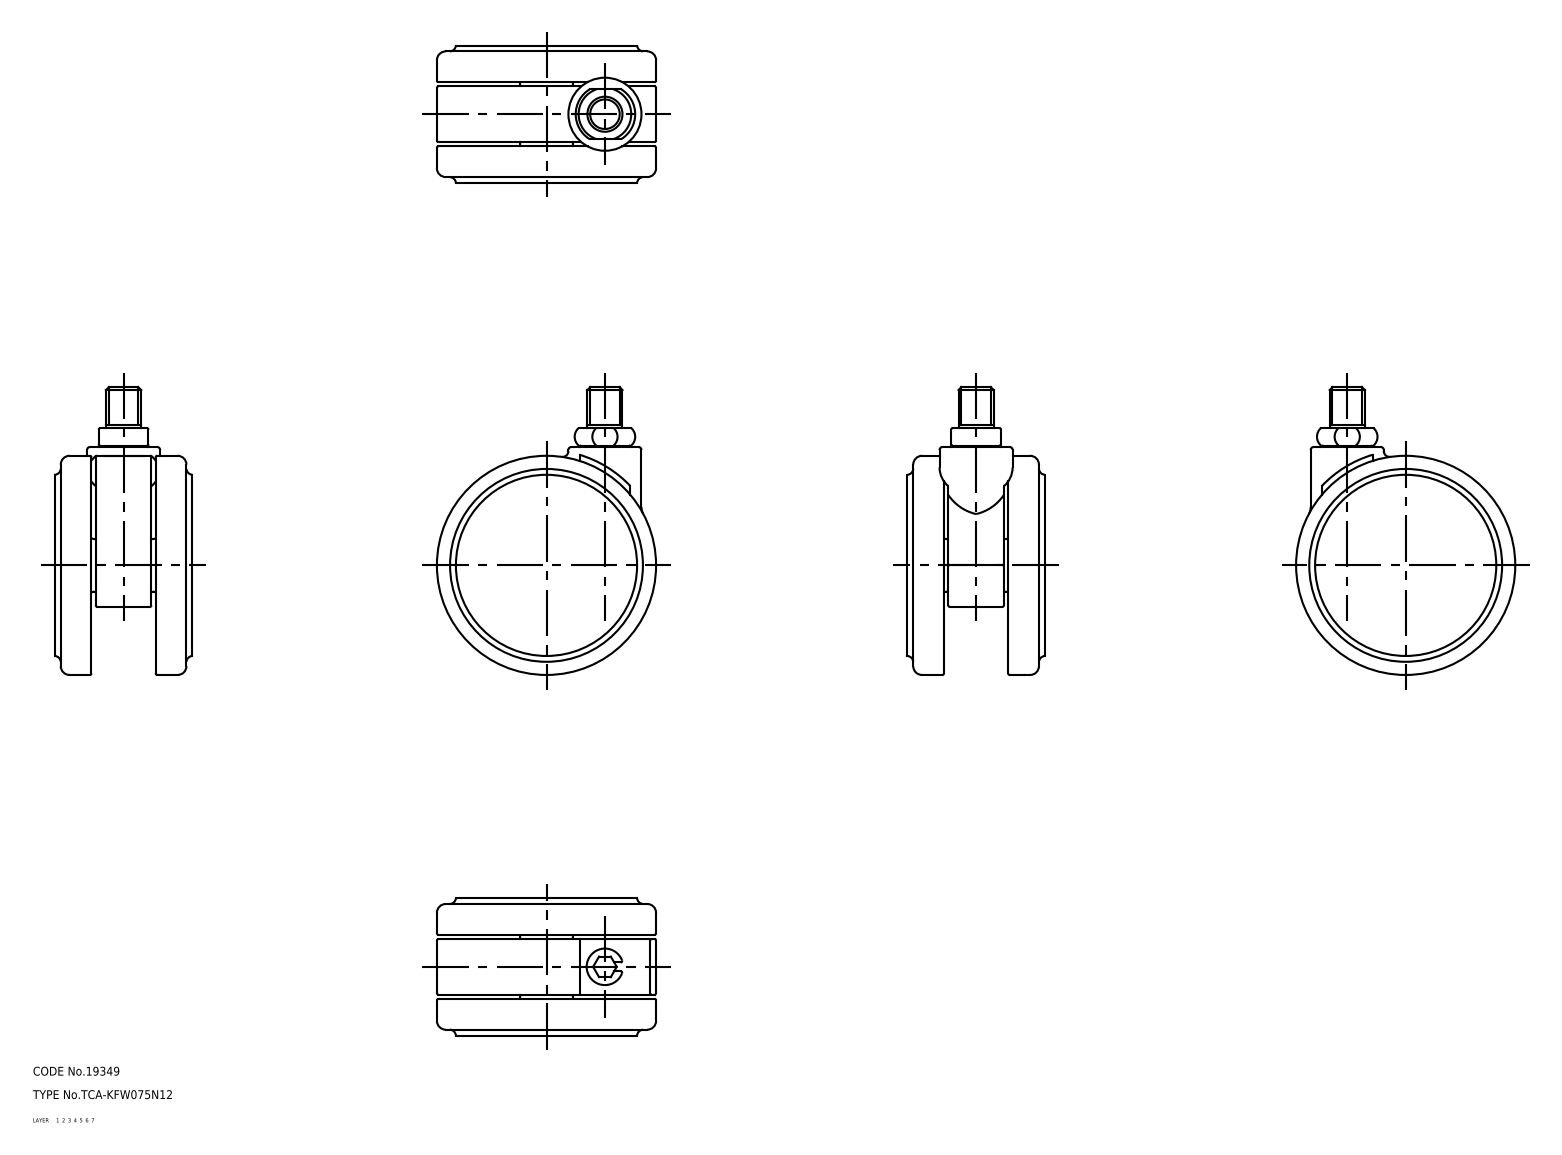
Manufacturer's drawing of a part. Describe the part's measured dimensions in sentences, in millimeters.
The part is named "main shaft; wheel_mr; wheel; TCA_KFW075N12". Its 3-D file was written by "SolidWorks 2015 (AUTOMOTIVE_DESIGN)". It is 4 solids with 126 faces: 35 planar, 45 cylindrical and 46 other. Overall it measures 98.5 by 75 by 47 millimeters. Its volume is 160 300 cubic millimeters and its surface area 36 969 square millimeters. Round holes: 1 of diameter 6, 1 of diameter 43. Round bosses or shafts: 1 of diameter 75, 1 of diameter 25, 1 of diameter 18, 1 of diameter 17, 1 of diameter 12.5, 1 of diameter 12. Partial cylindrical surfaces (rounded edges, fillets, slot ends): 13 of radius 0.5, 1 of radius 1, 1 of radius 2.89, 1 of radius 14.41, 1 of radius 39.5. The main face-to-face distances are 14, 33, 20.5, 1.5, 12.5, 34.5, 47, 19, 22, 25.
